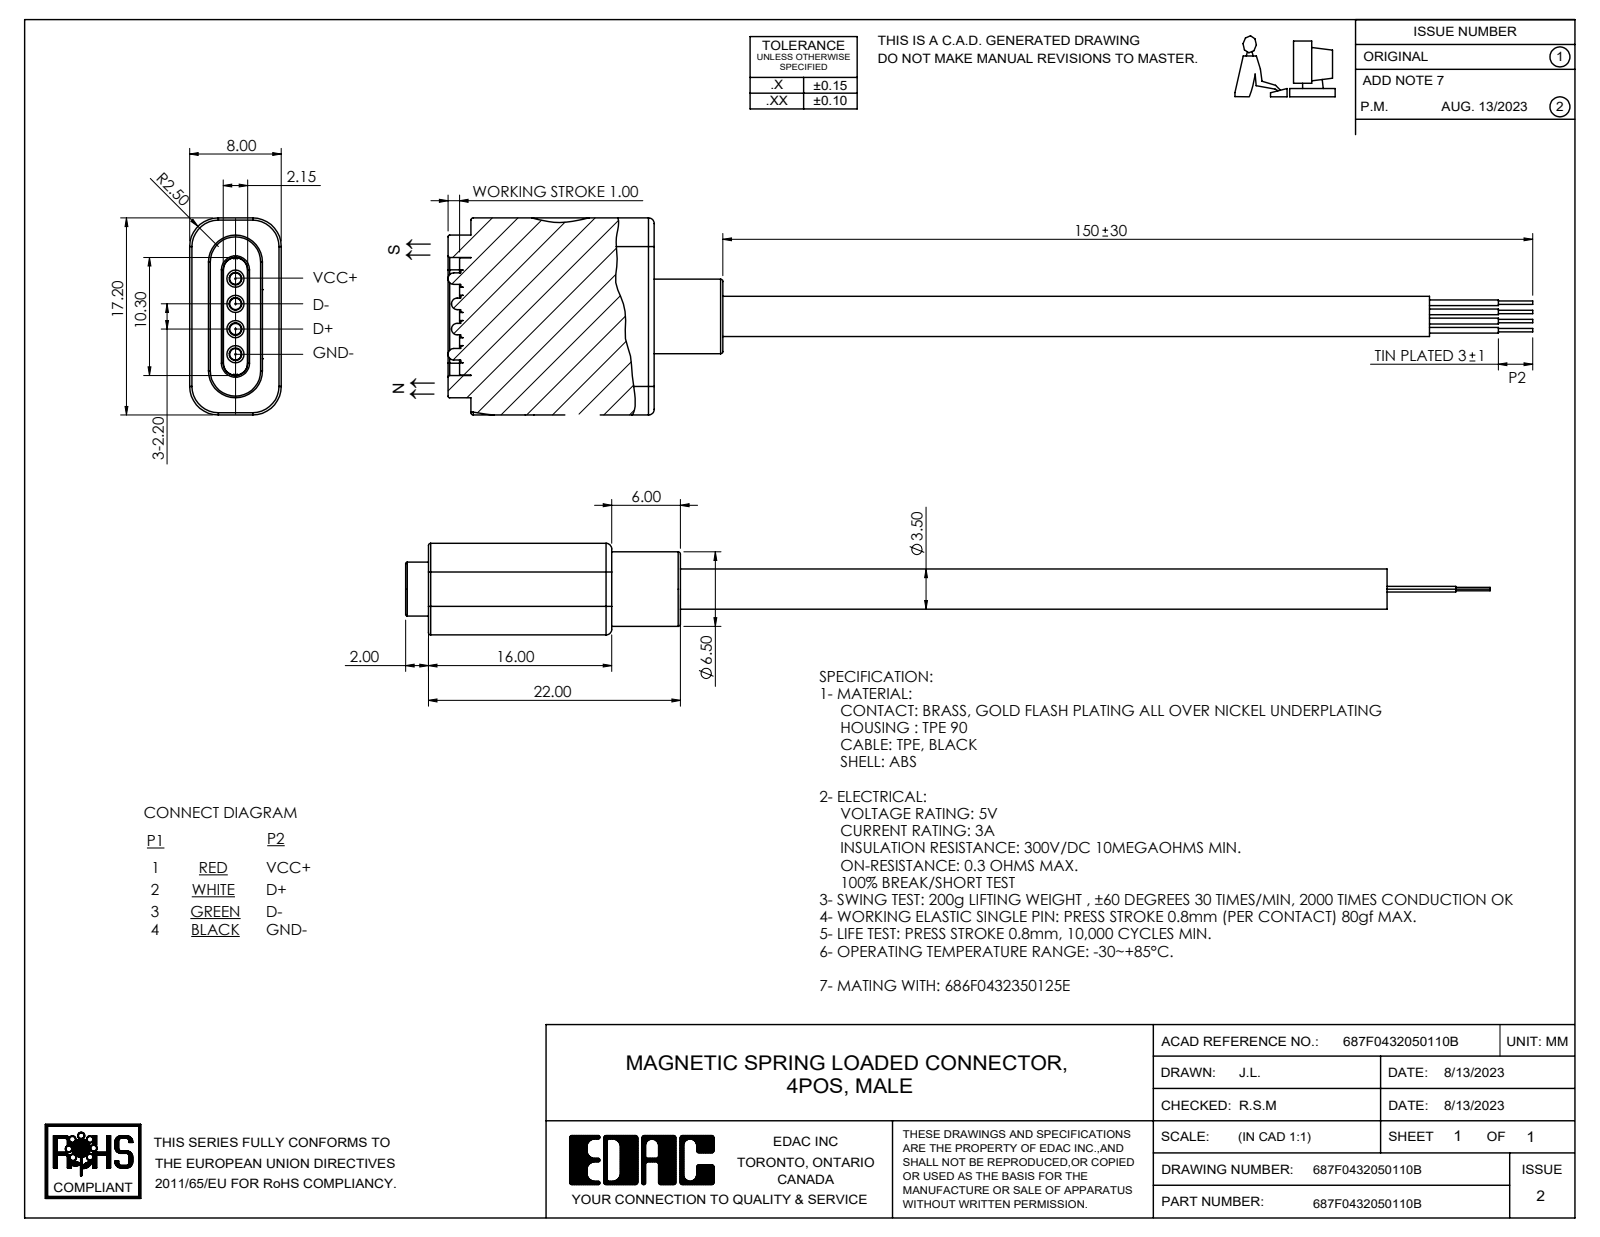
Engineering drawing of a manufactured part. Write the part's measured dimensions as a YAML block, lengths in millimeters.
part_name: "687F0432050110B"
step_written_by: "SolidWorks 2020 (AUTOMOTIVE_DESIGN)"
units: millimeters
bodies: {solids: 0, faces: 2694, planar: 1787, cylindrical: 135, other: 772}
overall_size: [94.7, 17.2, 8]
round_holes:
  - {diameter: 1.5, count: 6}
  - {diameter: 1.75, count: 4}
round_bosses_or_shafts:
  - {diameter: 1.7, count: 4}
  - {diameter: 1, count: 4}
  - {diameter: 0.5, count: 4}
  - {diameter: 0.3, count: 4}
  - {diameter: 6.5, count: 1}
  - {diameter: 3.5, count: 1}
partial_cylinders:
  - {radius: 1.7, count: 12}
  - {radius: 0.15, count: 8}
  - {radius: 0.2, count: 6}
  - {radius: 0.5, count: 4}
  - {radius: 1, count: 4}
  - {radius: 2.5, count: 4}
  - {radius: 0.1, count: 2}
  - {radius: 1.05, count: 2}
face_to_face_distances: [0.8, 7.2, 0.85, 6.4, 6.35, 8, 1.65, 5.55, 1.49, 16.4]
hole_center_spacings: [2.2, 2.71, 4.4, 4.79, 6.95, 9.12, 6.6, 11.73]
